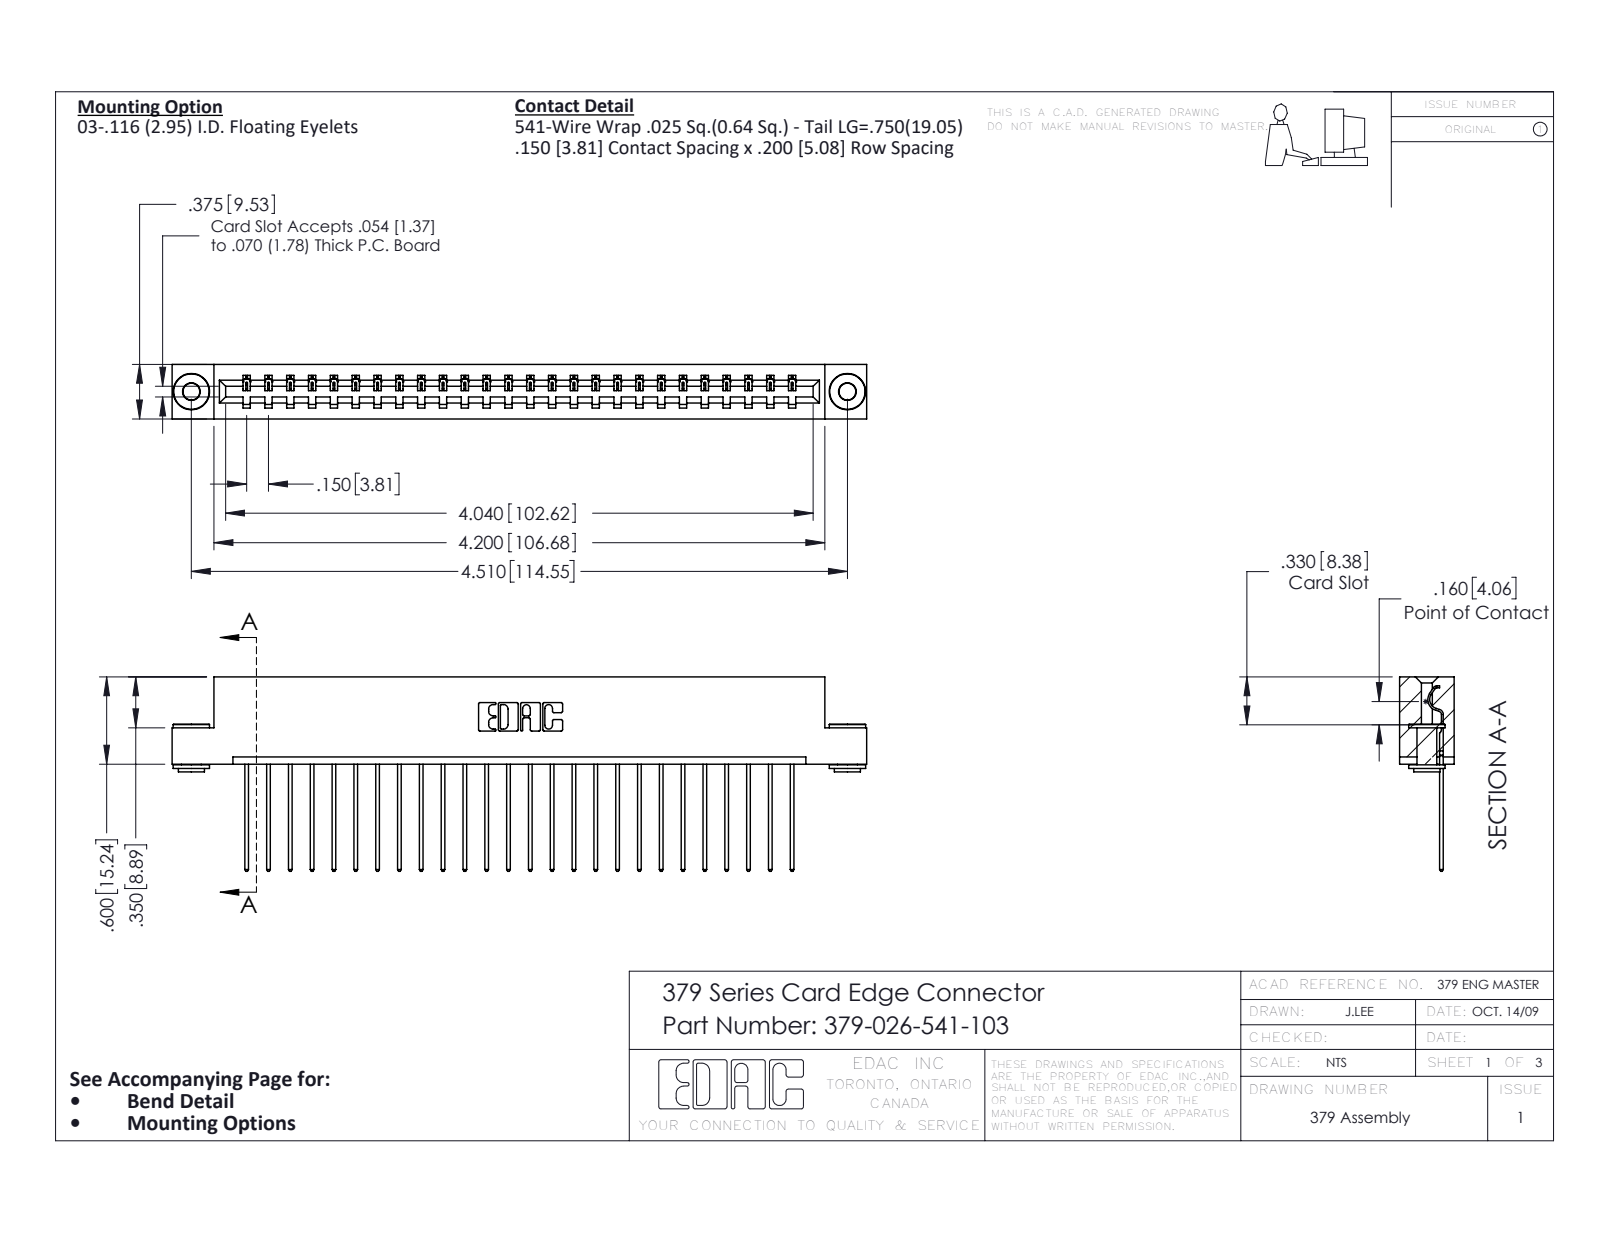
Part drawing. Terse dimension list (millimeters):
name: 345-250-002_345-250-002-102; 345-292-001_345-293-141; 379-026-541-103; 379 Part_Flush - .156 Dia - TH
written by: SolidWorks 2016 (CONFIG_CONTROL_DESIGN)
unit: mm
bodies: 29 solids, 1660 faces (1172 planar, 480 cylindrical, 8 other)
size: 121.3 × 34 × 9.5
volume: 12 700 mm³; area: 13 630 mm²
holes: 2× ⌀2.9, 2× ⌀4
bosses: 2× ⌀6.4, 2× ⌀4.6, 2× ⌀3.5
rounds: 52× R0.2, 52× R0.3, 22× R0.3, 6× R0.2, 6× R0.8, 3× R0.7, 1× R0.4, 1× R0.6
face distances: 7.6, 1.9, 9.5, 5.7, 7, 0.6, 15.2, 2.5, 5.1, 3.8
hole spacings: 114.6
